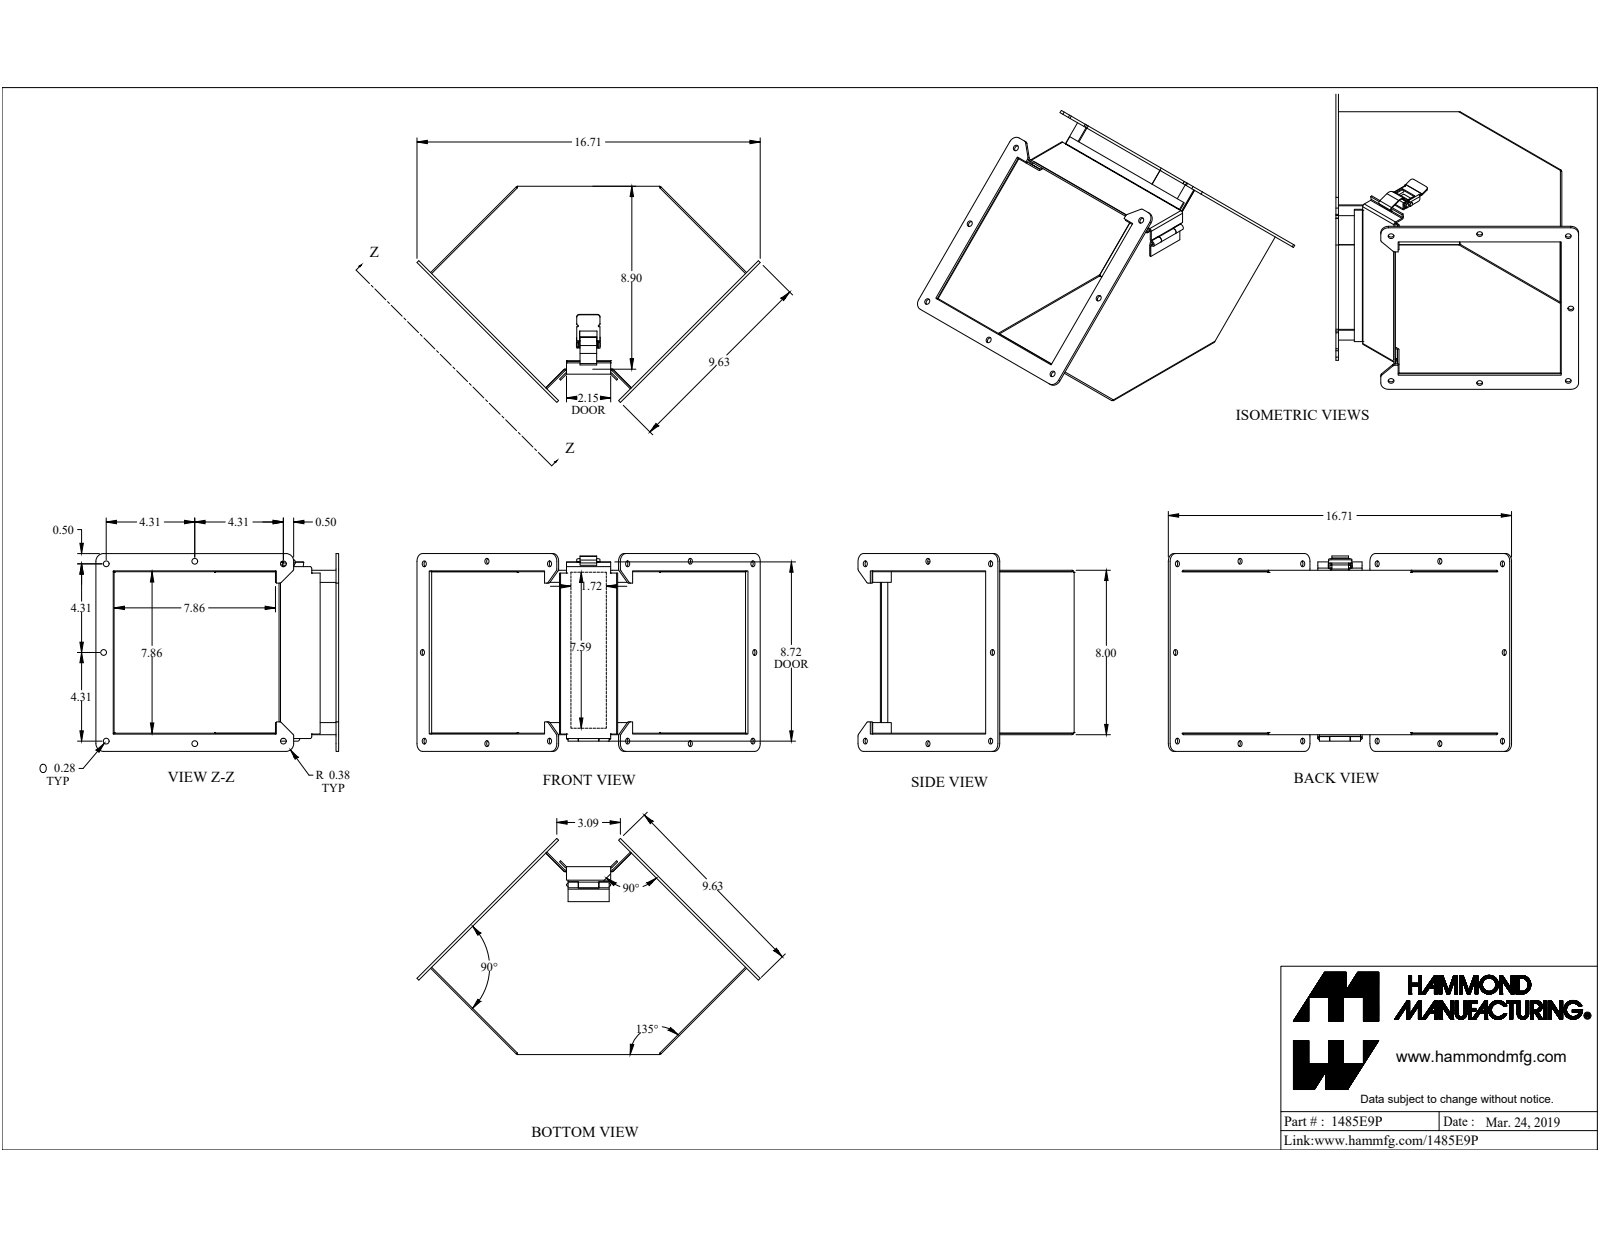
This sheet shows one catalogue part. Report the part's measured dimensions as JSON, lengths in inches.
{"part_name": "1485E9P", "step_written_by": "SolidWorks 2019 (CONFIG_CONTROL_DESIGN)", "units": "inches", "bodies": {"solids": 12, "faces": 339, "planar": 222, "cylindrical": 115, "other": 2}, "overall_size": [16.706, 10.517, 9.625], "volume_in3": 33.4, "surface_area_in2": 891.4, "round_holes": [[0.281, 14], [0.125, 1], [0.13, 1], [0.164, 1]], "round_bosses_or_shafts": [[0.187, 2], [0.275, 1], [0.156, 1], [0.125, 1], [0.125, 1]], "partial_cylinders_radius": [[0.036, 11], [0.108, 11], [0.125, 11], [0.375, 8], [0.016, 7], [0.035, 3], [0.039, 3], [0.076, 3]], "face_to_face_distances": [0.072, 7.928, 8, 7.856, 10.802, 10.874, 0.125, 10.926, 10.998, 9.07], "hole_center_spacings": [4.314, 9.755, 9.755, 4.315, 8.625, 8.625, 12.198, 6.276]}
